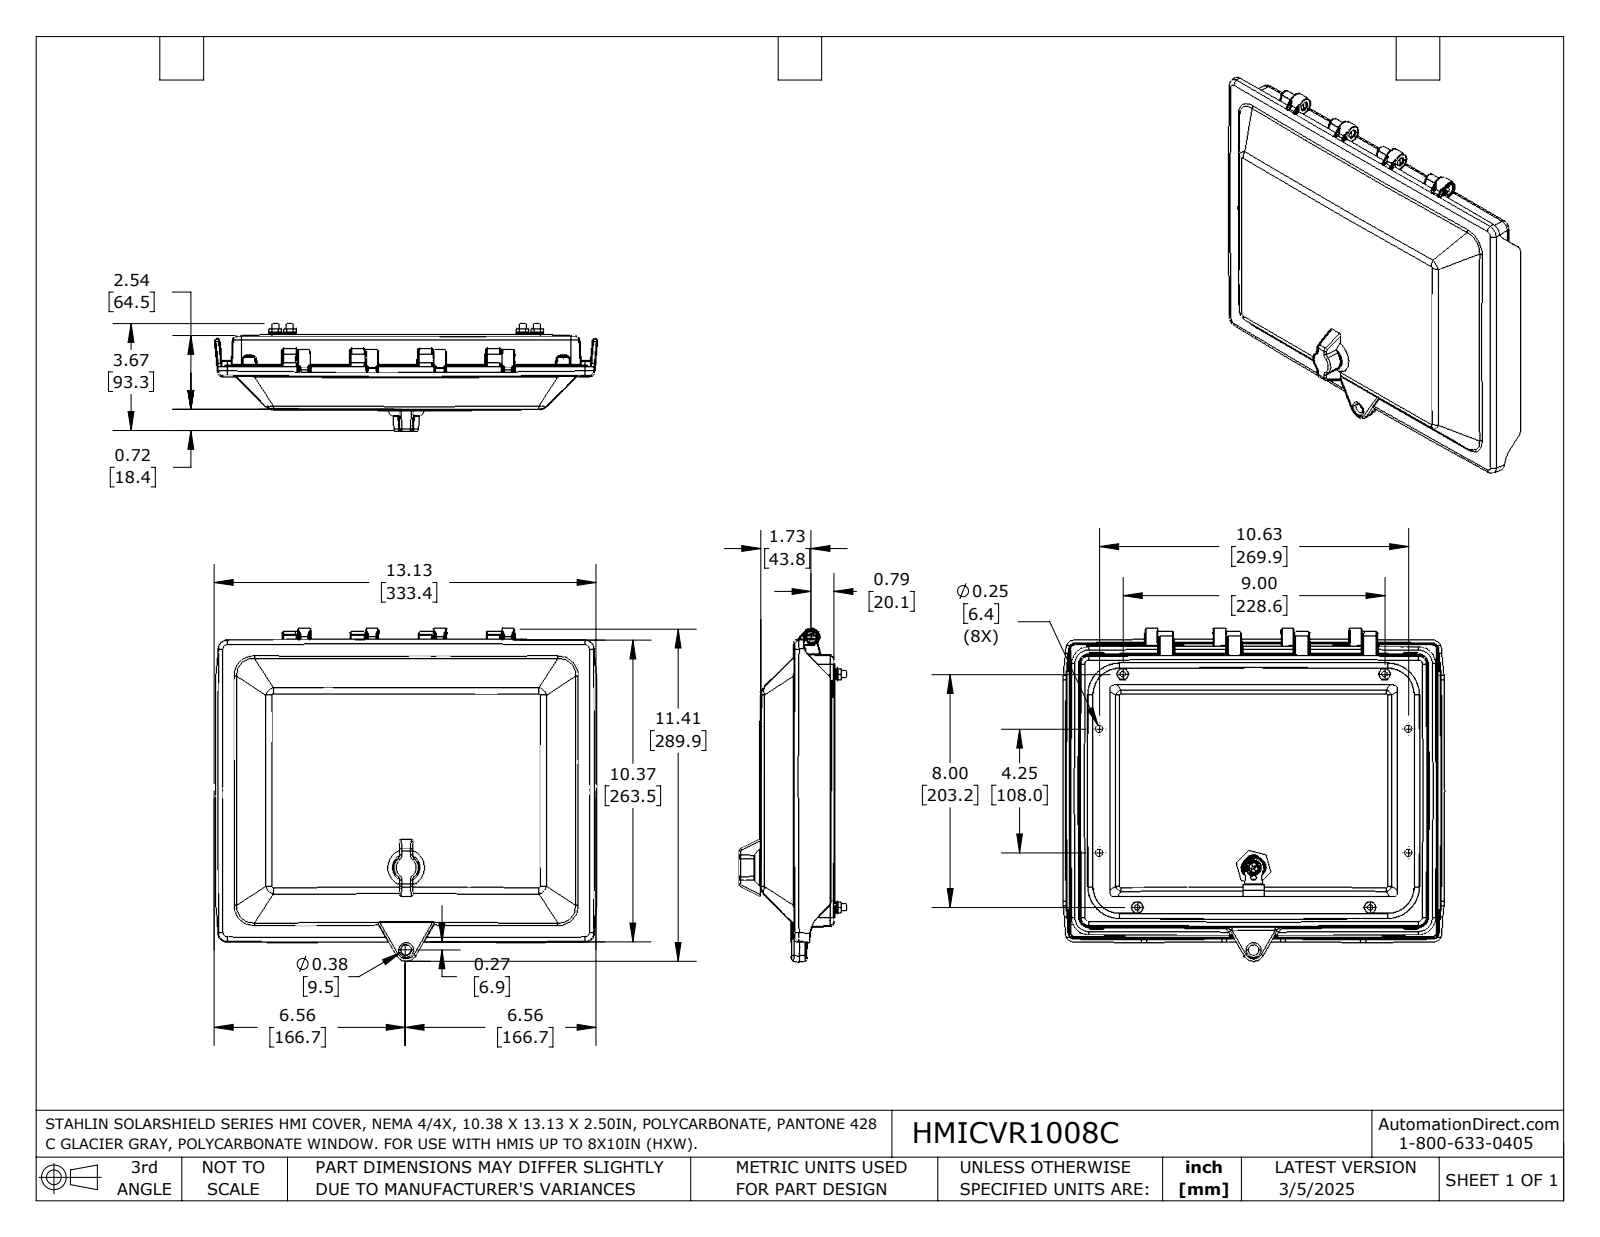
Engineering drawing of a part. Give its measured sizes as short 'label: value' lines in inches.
name: HMICVR1008C
written by: SolidWorks 2024 (AUTOMOTIVE_DESIGN)
unit: in
bodies: 25 solids, 1726 faces (454 planar, 309 cylindrical, 963 other)
size: 13.126 × 11.415 × 3.673
volume: 37.9 in³; area: 632.6 in²
holes: 5× ⌀0.197, 4× ⌀0.19, 2× ⌀0.188, 1× ⌀0.083, 1× ⌀0.201, 1× ⌀0.315, 1× ⌀0.327, 1× ⌀0.591, 1× ⌀0.802, 1× ⌀0.846
bosses: 4× ⌀0.394, 4× ⌀0.373, 1× ⌀1.26, 1× ⌀0.78, 1× ⌀0.531, 1× ⌀0.365, 1× ⌀0.313, 1× ⌀0.217
rounds: 53× R0.03, 43× R0.02, 26× R0.039, 20× R0.012, 20× R0.02, 6× R0.04, 6× R0.059, 4× R0.106
face distances: 0.125, 0.86, 0.985, 0.157, 0.035, 0.895, 1.02, 0.175, 1.435, 1.47
hole spacings: 4.227, 8.016, 8.016, 11.672, 0.185, 6, 8, 8.007
